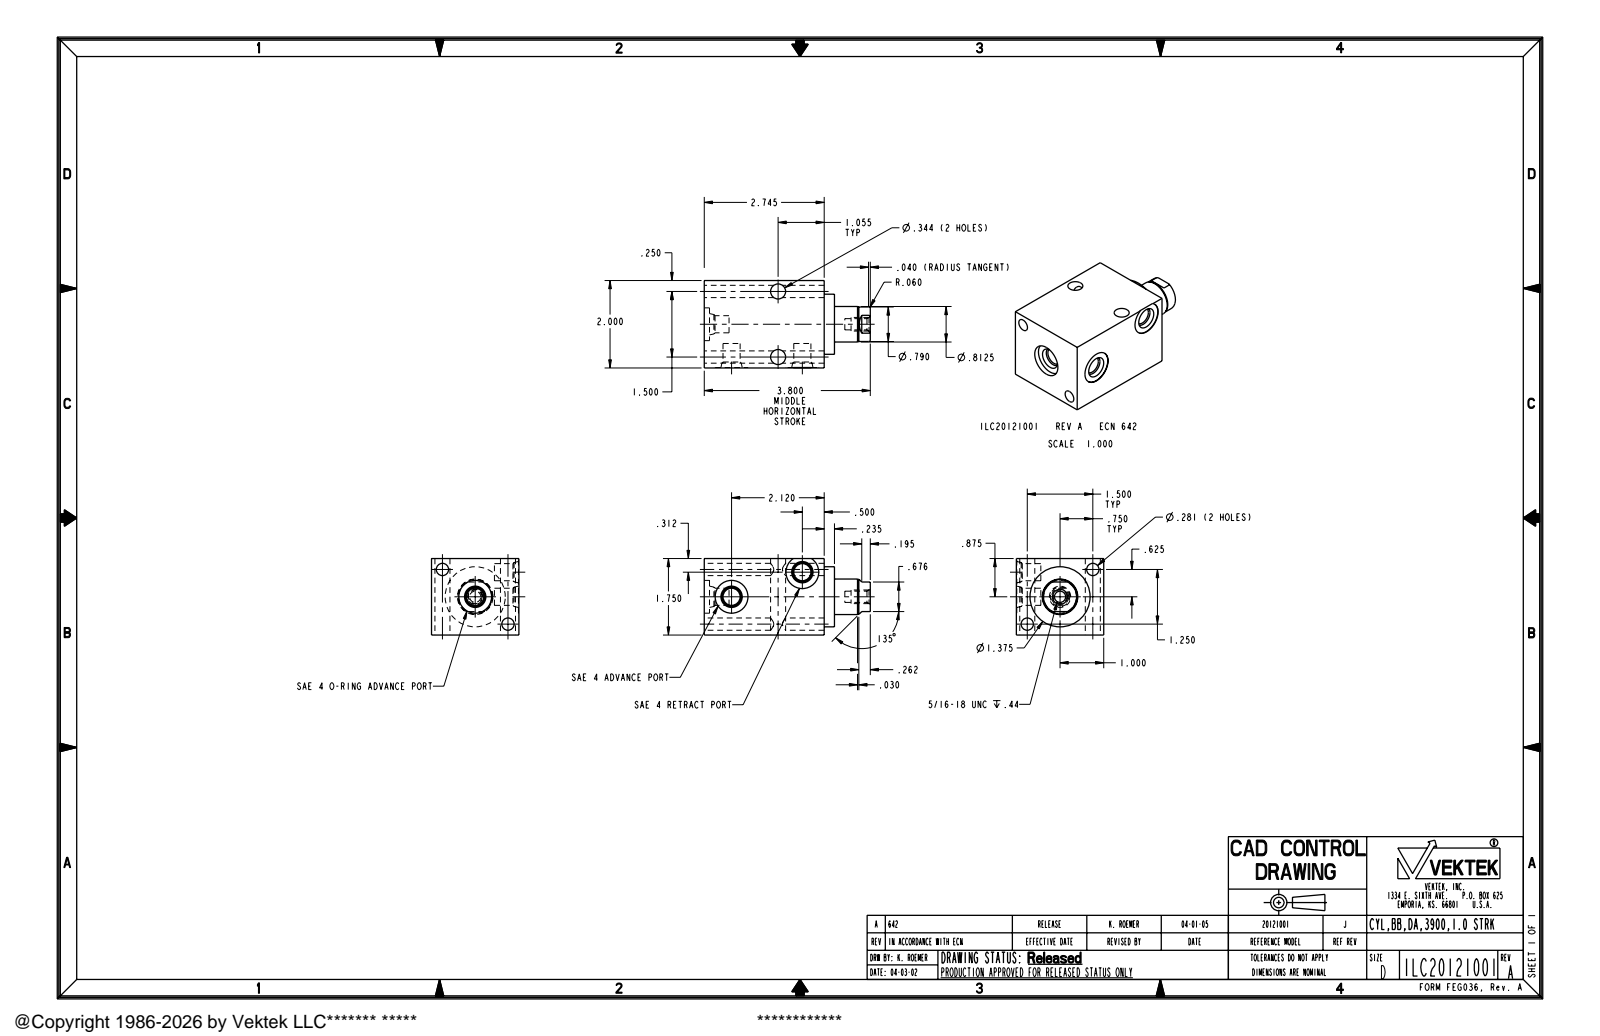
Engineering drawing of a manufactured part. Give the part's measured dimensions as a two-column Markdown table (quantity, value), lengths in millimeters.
| quantity | value |
| --- | --- |
| part name | ILC20121001 |
| STEP written by | PRO/ENGINEER BY PARAMETRIC TECHNOLOGY CORPORATION, 2004290 (AUTOMOTIVE_DESIGN_CC2) |
| units | millimeters |
| bodies | 1 solid, 71 faces (20 planar, 33 cylindrical, 18 other) |
| overall size | 96.5 × 50.8 × 44.5 |
| volume | 154 700 mm³ |
| surface area | 26 380 mm² |
| round holes (diameter × count) | 10 × 3, 19.1 × 3, 7.1 × 2, 8.7 × 2, 6.5 × 1 |
| round bosses / shafts (diameter × count) | 34.9 × 1, 20.7 × 1, 20.1 × 1, 7.9 × 1 |
| main face-to-face distances | 44.5, 50.8, 69.7, 6, 75.7, 50.5, 20.8, 26.8, 96.5, 93.5 |
| hole center spacings | 24.8, 38.1, 43.6, 49.6 |
